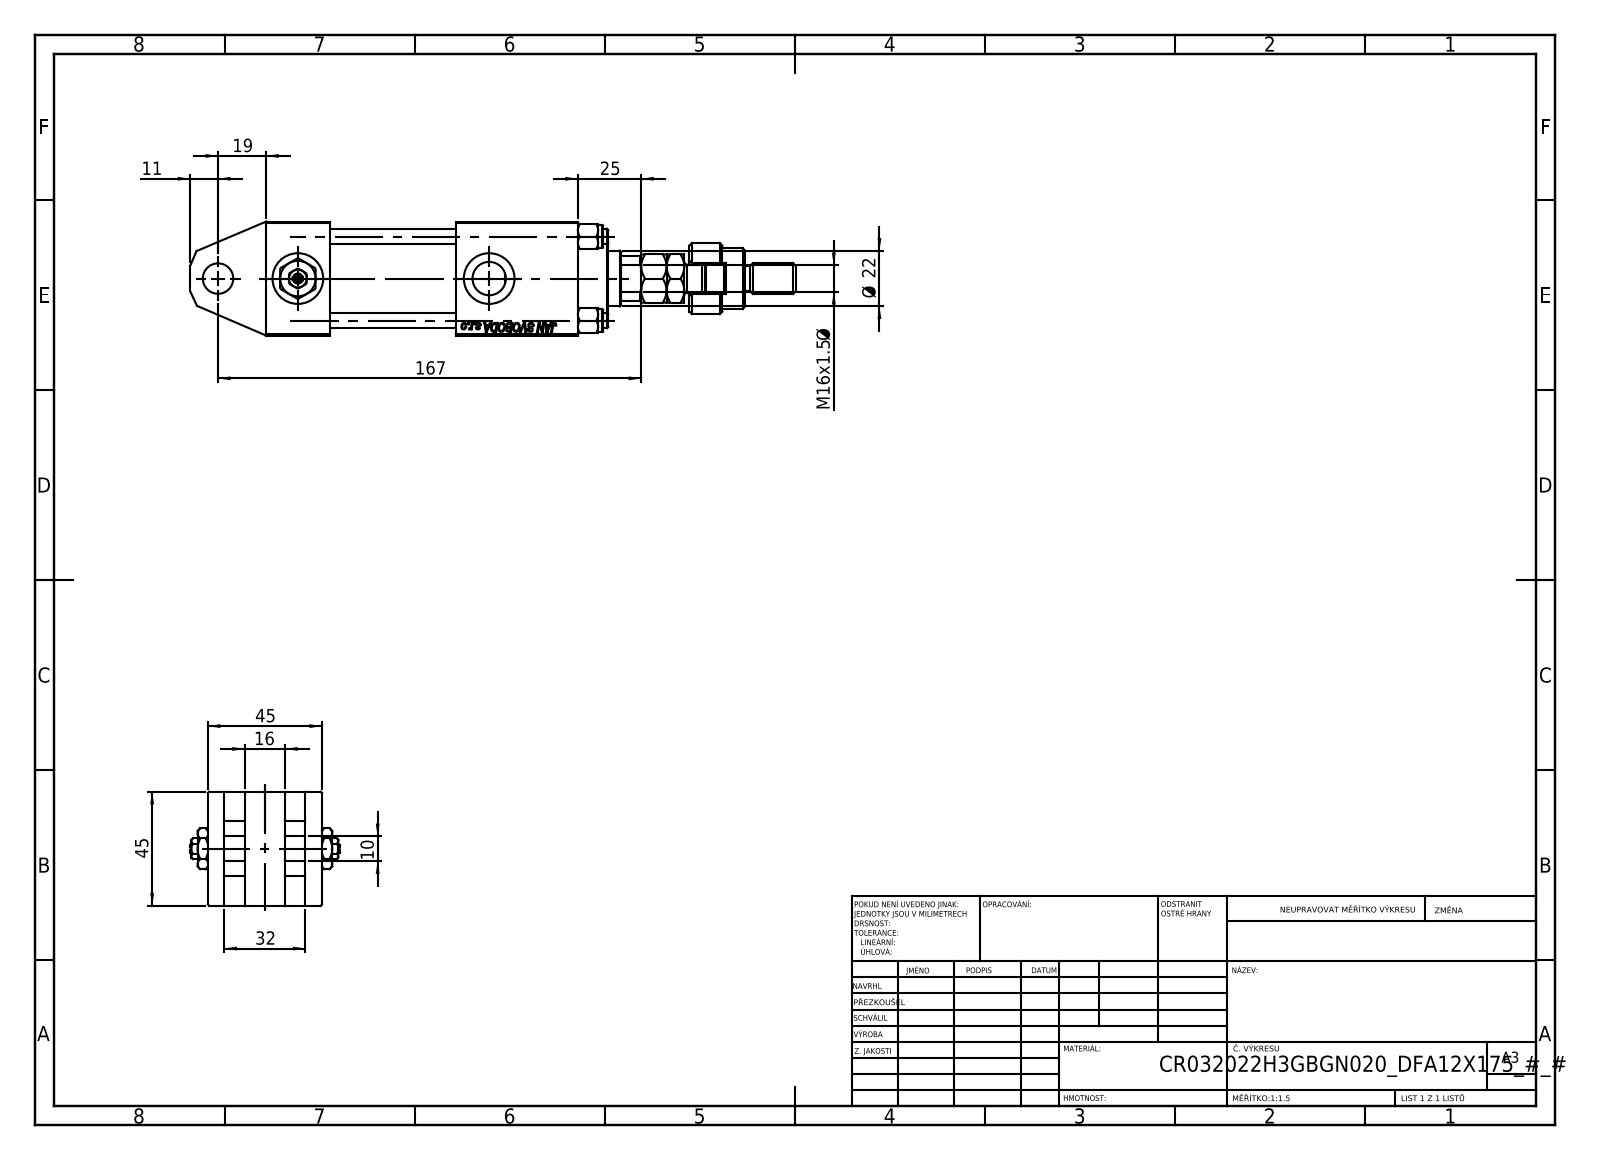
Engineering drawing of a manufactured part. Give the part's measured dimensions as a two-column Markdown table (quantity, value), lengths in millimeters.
| quantity | value |
| --- | --- |
| part name | V215CR_VCP_H; FEMALE_PART_FOR_DFA; V215_VC_A; MFA (+4 more) |
| STEP written by | SolidWorks 2019 (CONFIG_CONTROL_DESIGN) |
| units | millimeters |
| bodies | 15 solids, 1313 faces (592 planar, 107 cylindrical, 614 other) |
| overall size | 239 × 59 × 45 |
| volume | 241 162 mm³ |
| surface area | 87 385 mm² |
| round holes (diameter × count) | 6 × 4, 7 × 2, 13.16 × 2, 20 × 2, 10.5 × 1, 12 × 1, 22 × 1, 24 × 1, 25 × 1, 32 × 1, 33 × 1 |
| round bosses / shafts (diameter × count) | 9 × 4, 38 × 1, 34 × 1, 28 × 1, 18 × 1, 12 × 1, 11 × 1, 10 × 1 |
| partial cylindrical surfaces (radius × count) | 9.75 × 1, 10.5 × 1 |
| main face-to-face distances | 45, 8, 25, 14.5, 38.5, 24, 30.5, 6.5, 123, 32 |
| hole center spacings | 23.48, 33.2, 46.95, 31.5, 75.5, 107 |
